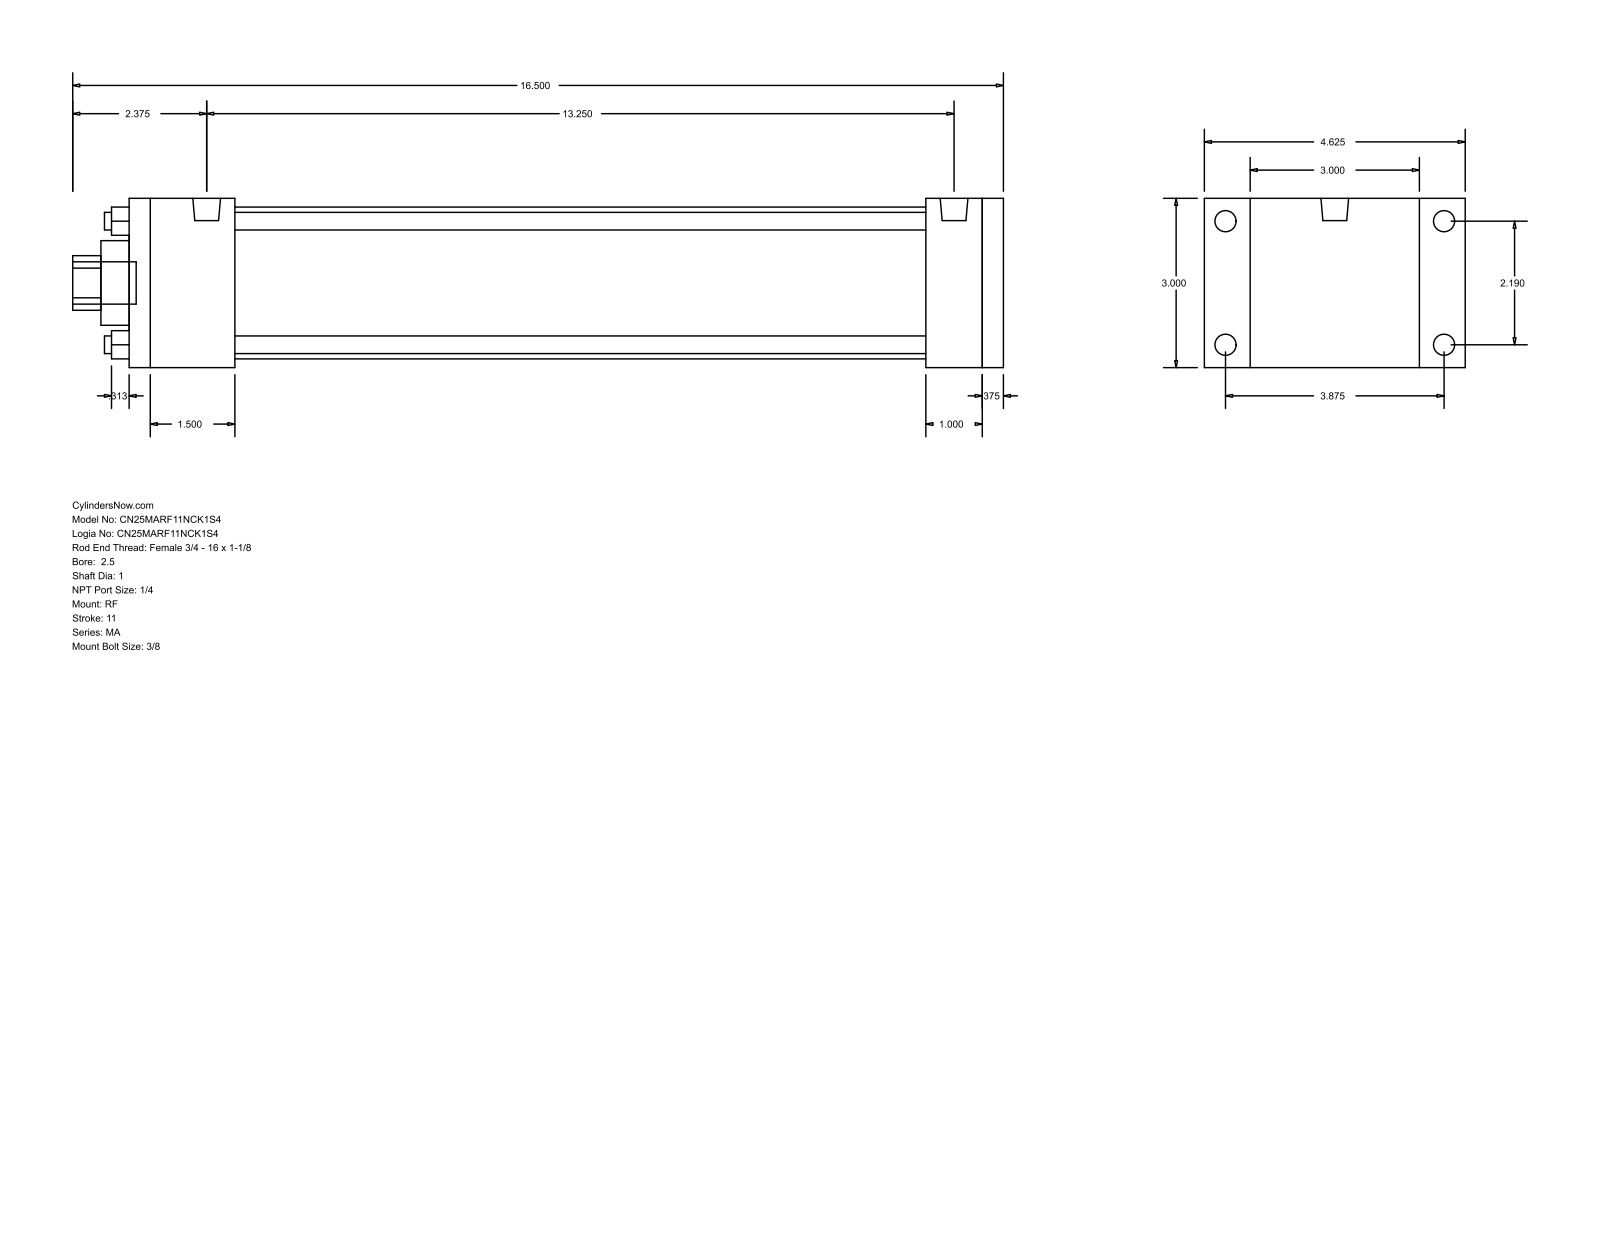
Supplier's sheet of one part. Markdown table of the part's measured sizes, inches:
| quantity | value |
| --- | --- |
| part name | MA_RF__0250_1 |
| STEP written by | GSSL Pune (CONFIG_CONTROL_DESIGN) |
| units | inches |
| bodies | 0 solids, 92 faces (64 planar, 28 cylindrical, 0 other) |
| overall size | 16.5 × 4.625 × 3 |
| round holes (diameter × count) | 0.313 × 4, 1 × 1, 1.5 × 1, 2.69 × 1 |
| round bosses / shafts (diameter × count) | 0.375 × 4, 0.313 × 4, 0.492 × 2, 0.75 × 1 |
| partial cylindrical surfaces (radius × count) | 0.484 × 1 |
| main face-to-face distances | 3, 15.5, 0.375, 15.125, 1.875, 14.125, 12.25, 13.25, 13.625, 1 |
| hole center spacings | 1.548, 2.19, 3.097 |
